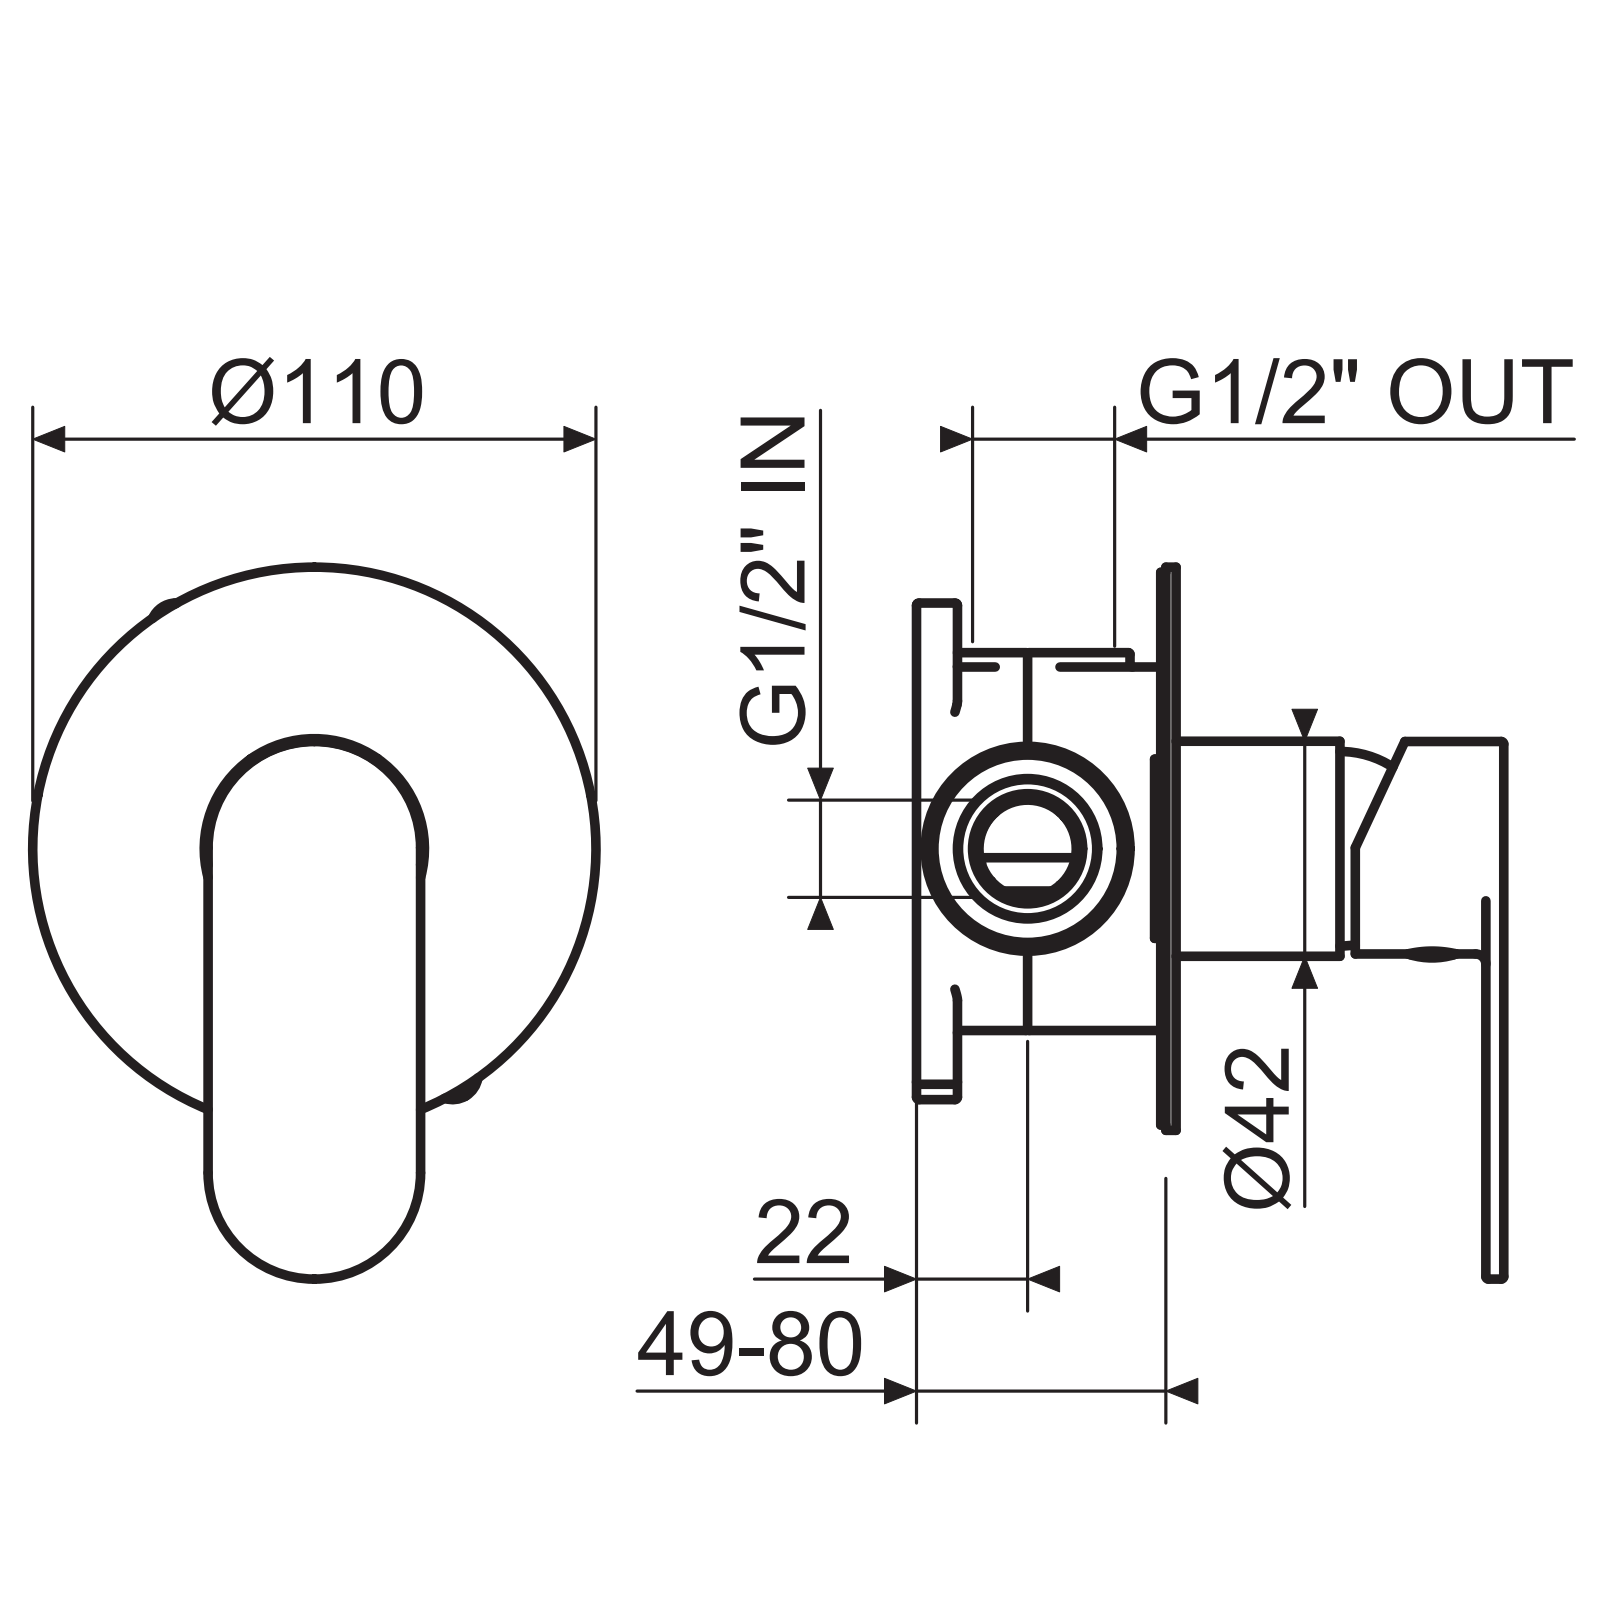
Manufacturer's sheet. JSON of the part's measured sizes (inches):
{"part_name": "SINMAC0008; SCCMAC0005; AUNO005C002; SPLMAC0004 (+4 more)", "step_written_by": "CREO PARAMETRIC BY PTC INC, 2020281 (CONFIG_CONTROL_DESIGN)", "units": "inches", "bodies": {"solids": 6, "faces": 289, "planar": 73, "cylindrical": 106, "other": 110}, "overall_size": [5.482, 4.331, 2.776], "volume_in3": 2.686, "surface_area_in2": 76.48, "round_holes": [[0.039, 2], [0.315, 2], [0.165, 1], [0.201, 1], [0.217, 1], [0.256, 1], [1.142, 1], [1.289, 1], [1.358, 1], [1.575, 1], [1.693, 1], [1.713, 1]], "round_bosses_or_shafts": [[4.331, 1], [1.929, 1], [1.654, 1], [1.634, 1], [1.339, 1], [0.362, 1], [0.197, 1]], "partial_cylinders_radius": [[0.02, 27], [0.039, 6], [0.063, 6], [0.059, 2], [0.118, 2], [0.148, 1], [0.154, 1], [0.817, 1]], "face_to_face_distances": [0.079, 2.539, 2.618, 0.138, 2.48, 2.402, 0.157, 2.461, 0.059, 0.236]}
